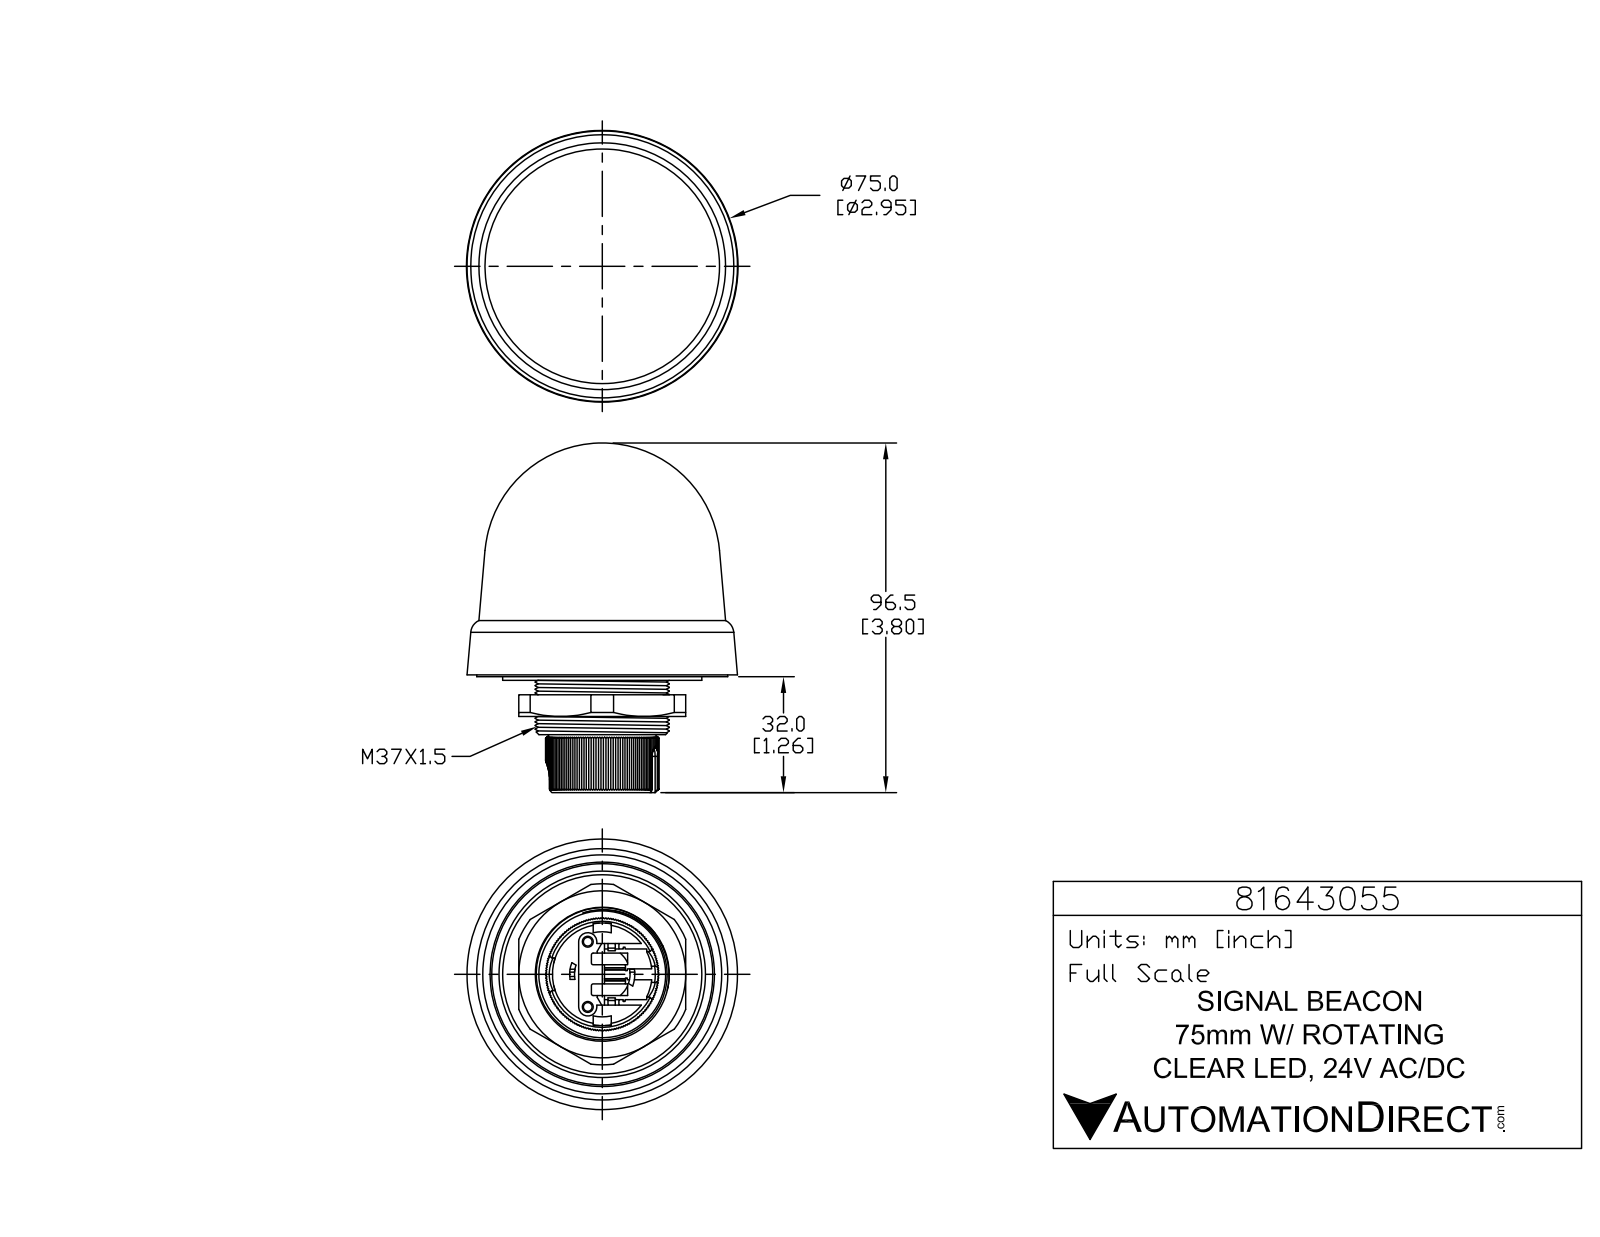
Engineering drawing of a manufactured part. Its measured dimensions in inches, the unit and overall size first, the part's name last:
Units: inches
Overall size (bounding box): 3.799 × 2.941 × 2.941
Round holes (diameter × count): ⌀0.094 ×2, ⌀0.118 ×2, ⌀0.604 ×1, ⌀1.142 ×1
Round bosses / shafts (diameter × count): ⌀0.217 ×2, ⌀0.067 ×2, ⌀2.165 ×1, ⌀1.457 ×1, ⌀0.925 ×1
Partial cylindrical surfaces — rounded edges, fillets, slot ends (radius × count): R0.008 ×6, R0.039 ×6, R0.02 ×4, R0.031 ×2, R0.079 ×2, R0.098 ×2, R0.177 ×1, R0.354 ×1
Main face-to-face distances: 0.177, 0.354, 0.197, 0.433, 0.512, 0.335, 0.059, 0.394, 0.118, 0.157
Hole centre spacings: 0.388, 0.709
Volume: 12.36 in³ · Surface area: 58.68 in²
Bodies: 3 solids, 560 faces (432 planar, 80 cylindrical, 48 other)
Part name (STEP PRODUCT): 81643055
STEP written by: SolidWorks 2019 (CONFIG_CONTROL_DESIGN)
